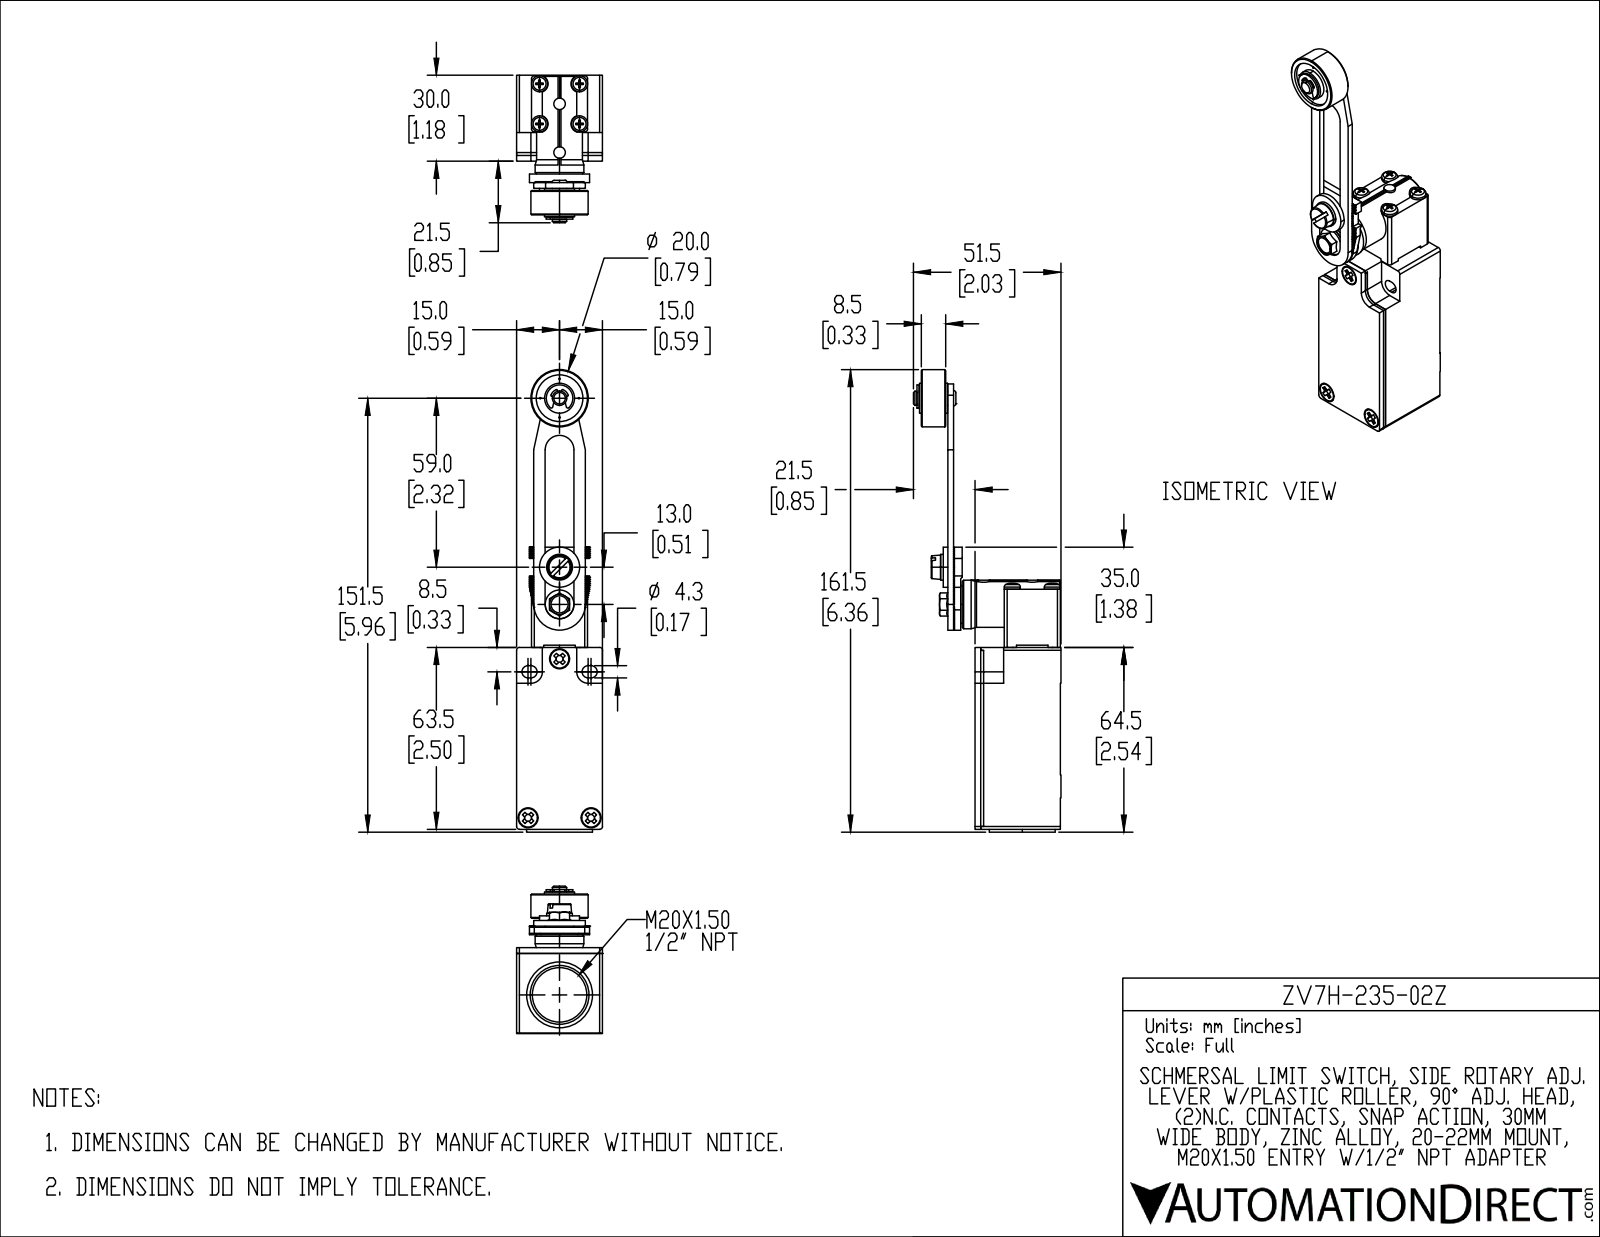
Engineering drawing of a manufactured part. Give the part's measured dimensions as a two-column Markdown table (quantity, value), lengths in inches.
| quantity | value |
| --- | --- |
| part name | ZV7H-235-02Z |
| STEP written by | SolidWorks 2019 (AUTOMOTIVE_DESIGN) |
| units | inches |
| bodies | 1 solid, 753 faces (547 planar, 160 cylindrical, 46 other) |
| overall size | 6.358 × 2.028 × 1.181 |
| volume | 4.272 in³ |
| surface area | 29.94 in² |
| round holes (diameter × count) | 0.02 × 4, 0.276 × 3, 0.154 × 1, 0.236 × 1, 0.512 × 1, 0.642 × 1, 0.748 × 1 |
| round bosses / shafts (diameter × count) | 0.221 × 4, 0.213 × 4, 0.157 × 4, 0.256 × 3, 0.394 × 2, 0.906 × 1, 0.787 × 1, 0.669 × 1 |
| partial cylindrical surfaces (radius × count) | 0.02 × 12, 0.039 × 8, 0.012 × 4, 0.059 × 4, 0.085 × 4, 0.118 × 4, 0.02 × 2, 0.157 × 2 |
| main face-to-face distances | 1.181, 1.173, 0.374, 0.295, 1.547, 0.079, 0.205, 1.469, 0.976, 0.772 |
| hole center spacings | 0.266, 0.376, 0.531, 2.228, 2.338, 2.848, 2.965, 3.472 |
